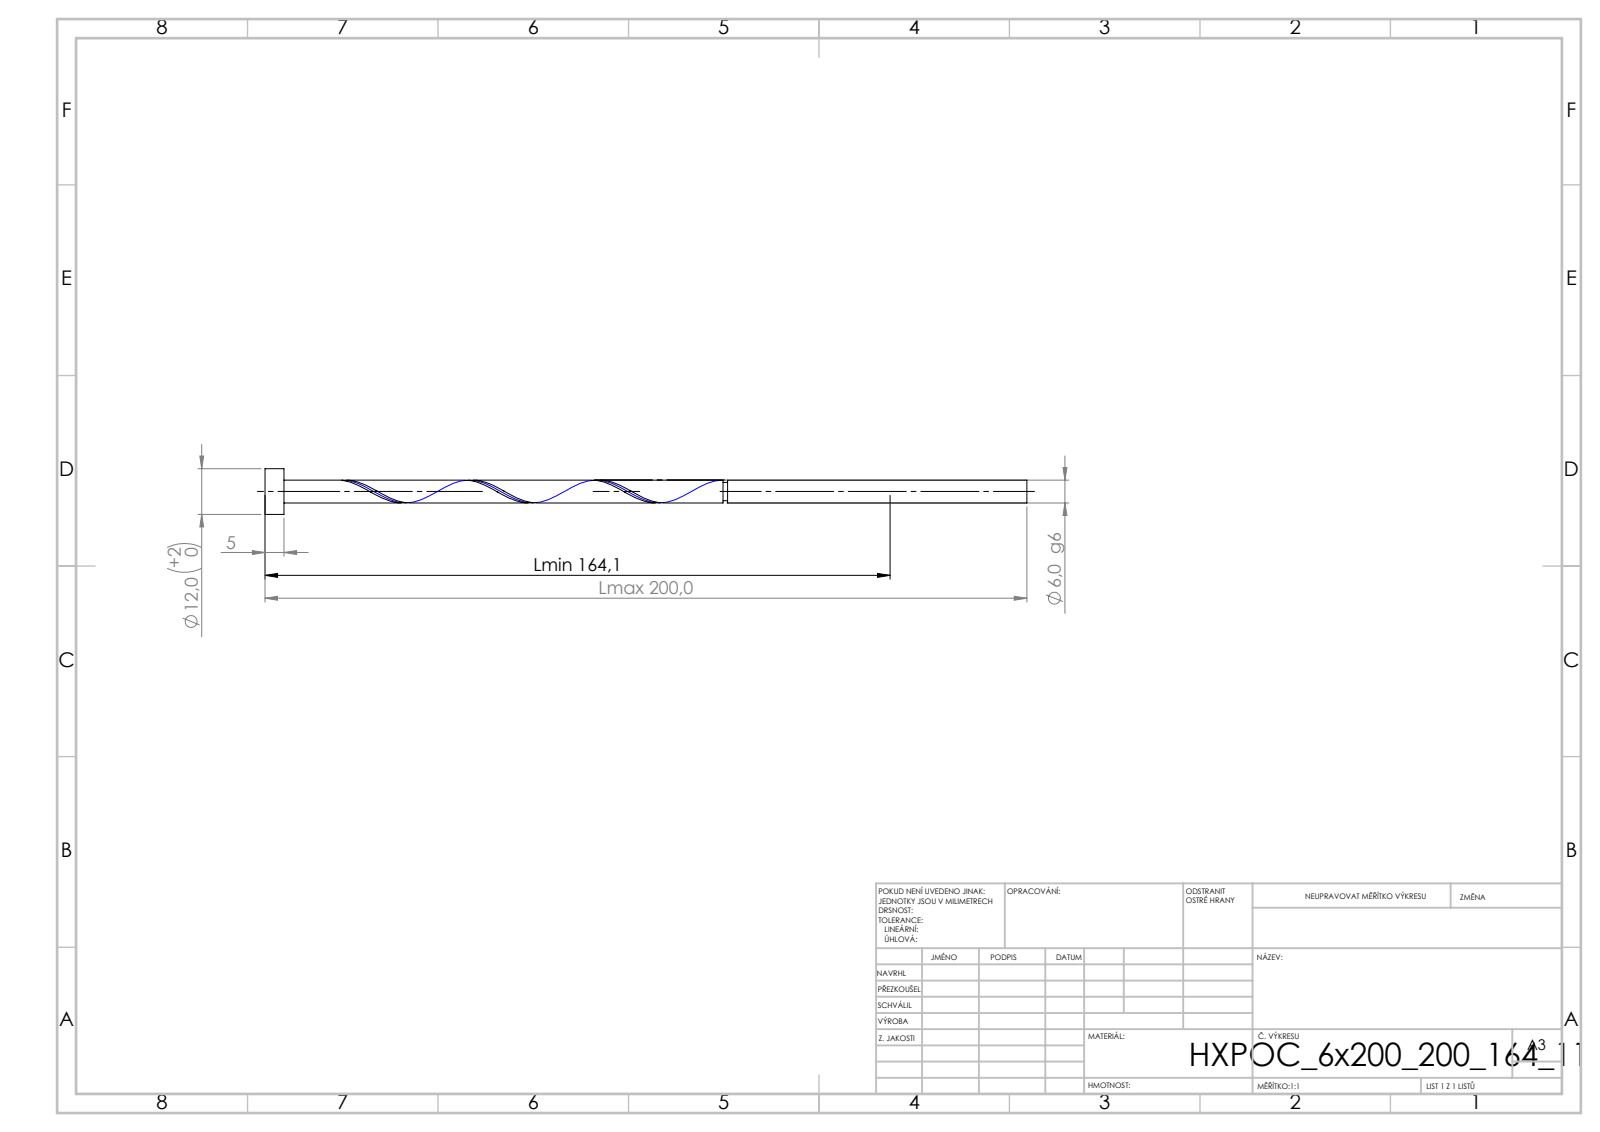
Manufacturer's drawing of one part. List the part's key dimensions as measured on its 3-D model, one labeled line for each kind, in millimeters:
STEP written by: SolidWorks 2019 (CONFIG_CONTROL_DESIGN)
Units: millimetres
Bodies: 1 solid, 21 faces (6 planar, 14 cylindrical, 1 other)
Overall size (bounding box): 200 × 12 × 12
Volume: 6 013 mm³ · Surface area: 4 175 mm²
Round bosses / shafts (diameter × count): ⌀12 ×1, ⌀6 ×1, ⌀4.8 ×1
Main face-to-face distances: 5, 200, 195, 121.44, 116.44, 78.56, 120.24, 115.24, 1.2, 79.76
